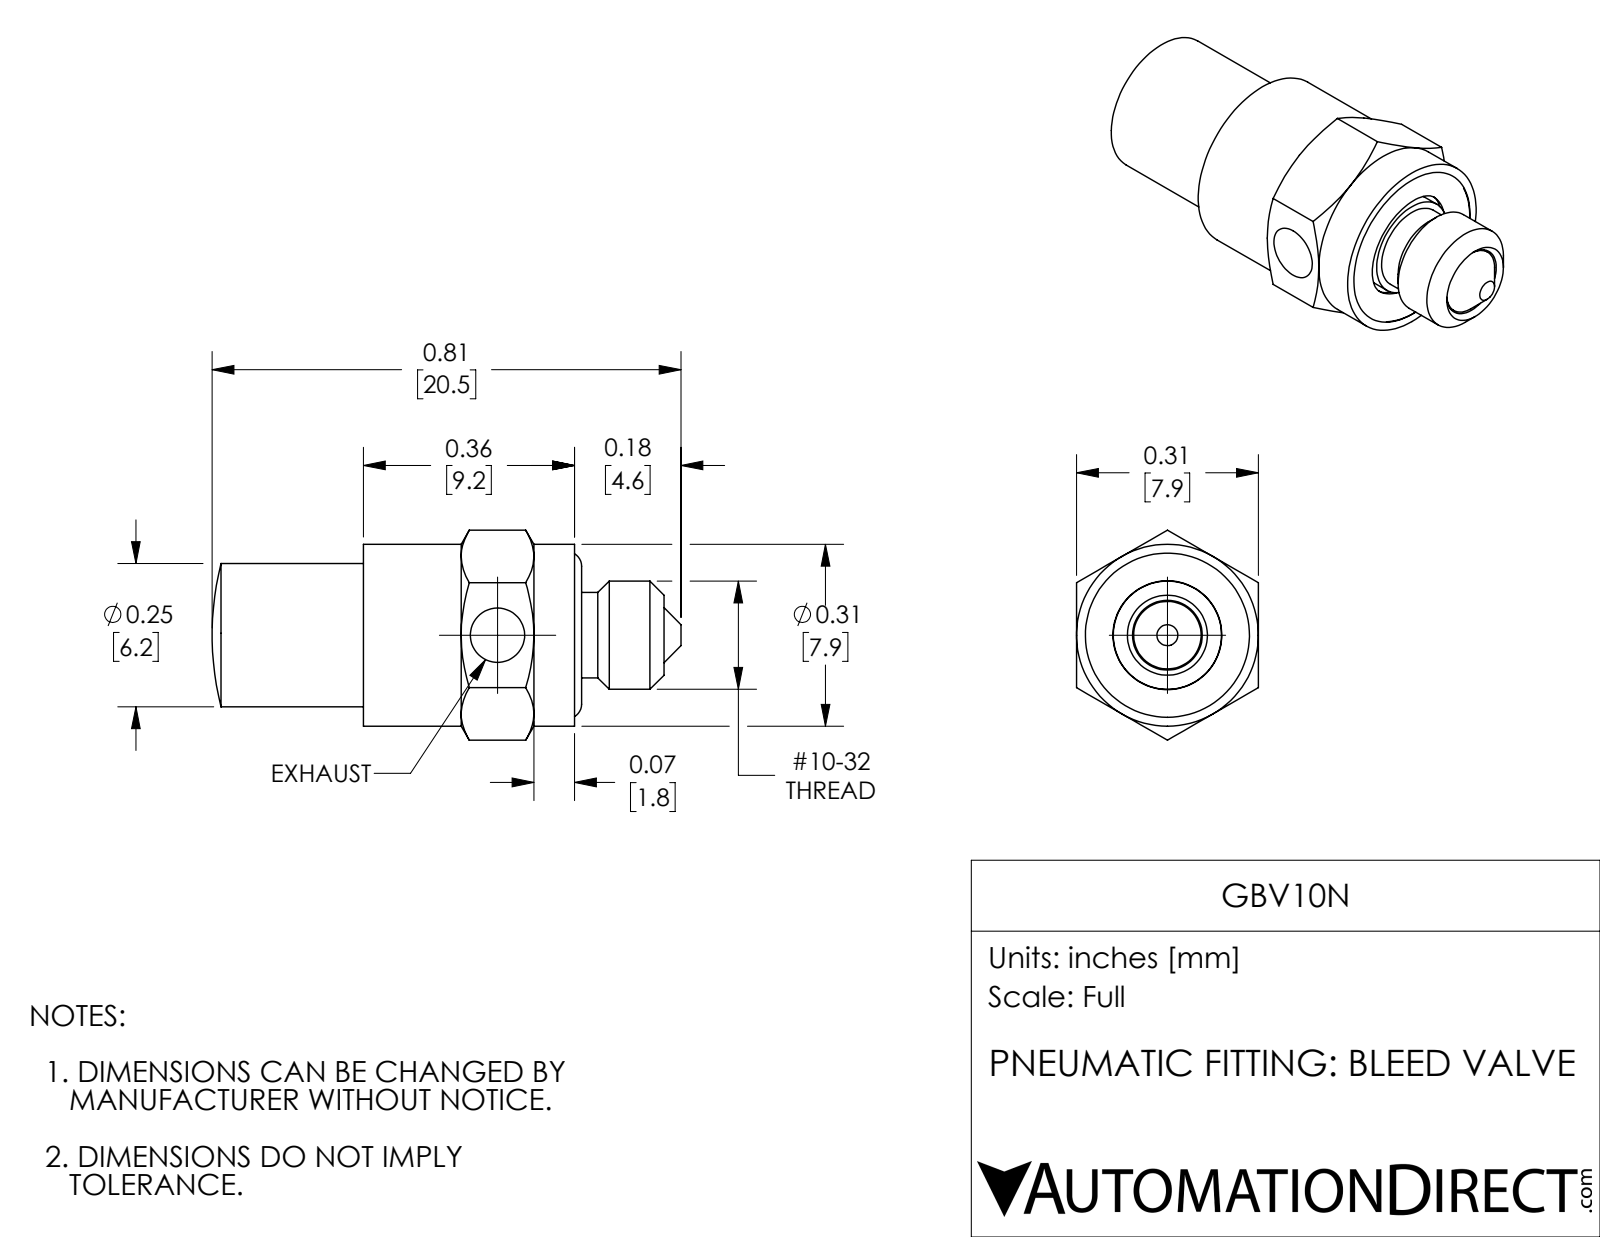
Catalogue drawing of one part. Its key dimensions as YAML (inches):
part_name: "GBV10N"
step_written_by: "SolidWorks 2018 (AUTOMOTIVE_DESIGN)"
units: inches
bodies: {solids: 5, faces: 66, planar: 16, cylindrical: 22, other: 28}
overall_size: [0.806, 0.361, 0.313]
volume: 0.035
surface_area: 1.418
round_holes:
  - {diameter: 0.093, count: 1}
  - {diameter: 0.12, count: 1}
  - {diameter: 0.25, count: 1}
  - {diameter: 0.282, count: 1}
round_bosses_or_shafts:
  - {diameter: 0.313, count: 1}
  - {diameter: 0.246, count: 1}
  - {diameter: 0.186, count: 1}
  - {diameter: 0.171, count: 1}
  - {diameter: 0.147, count: 1}
  - {diameter: 0.116, count: 1}
face_to_face_distances: [0.313, 0.164, 0.13, 0.294, 0.038, 0.168, 0.332, 0.363, 0.325, 0.195]
